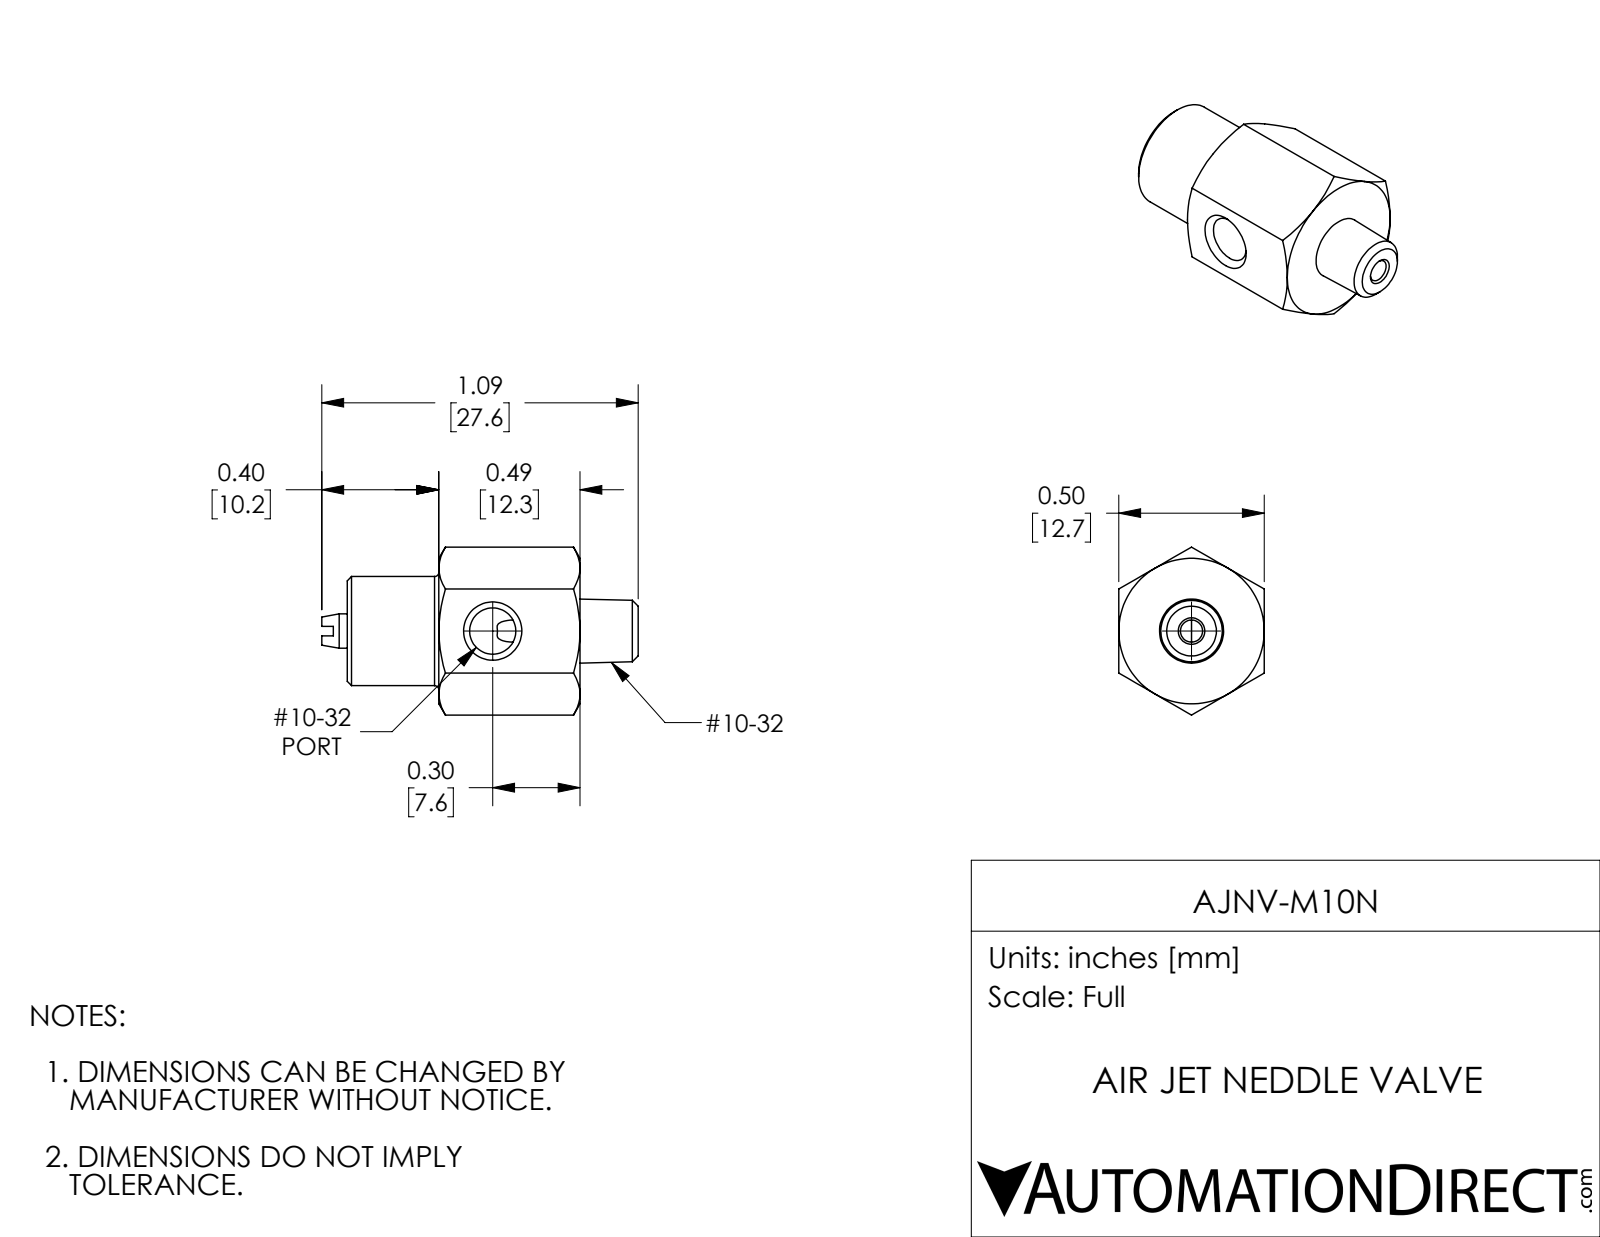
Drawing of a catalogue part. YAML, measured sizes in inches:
part_name: "AJNV-M10N"
step_written_by: "SolidWorks 2018 (AUTOMOTIVE_DESIGN)"
units: inches
bodies: {solids: 1, faces: 53, planar: 15, cylindrical: 8, other: 30}
overall_size: [1.088, 0.577, 0.5]
volume: 0.14
surface_area: 1.979
round_holes:
  - {diameter: 0.076, count: 1}
  - {diameter: 0.159, count: 1}
round_bosses_or_shafts:
  - {diameter: 0.375, count: 1}
  - {diameter: 0.118, count: 1}
face_to_face_distances: [0.5, 0.8, 0.315, 0.485, 1, 0.685, 0.2, 0.087, 0.402, 0.887]
